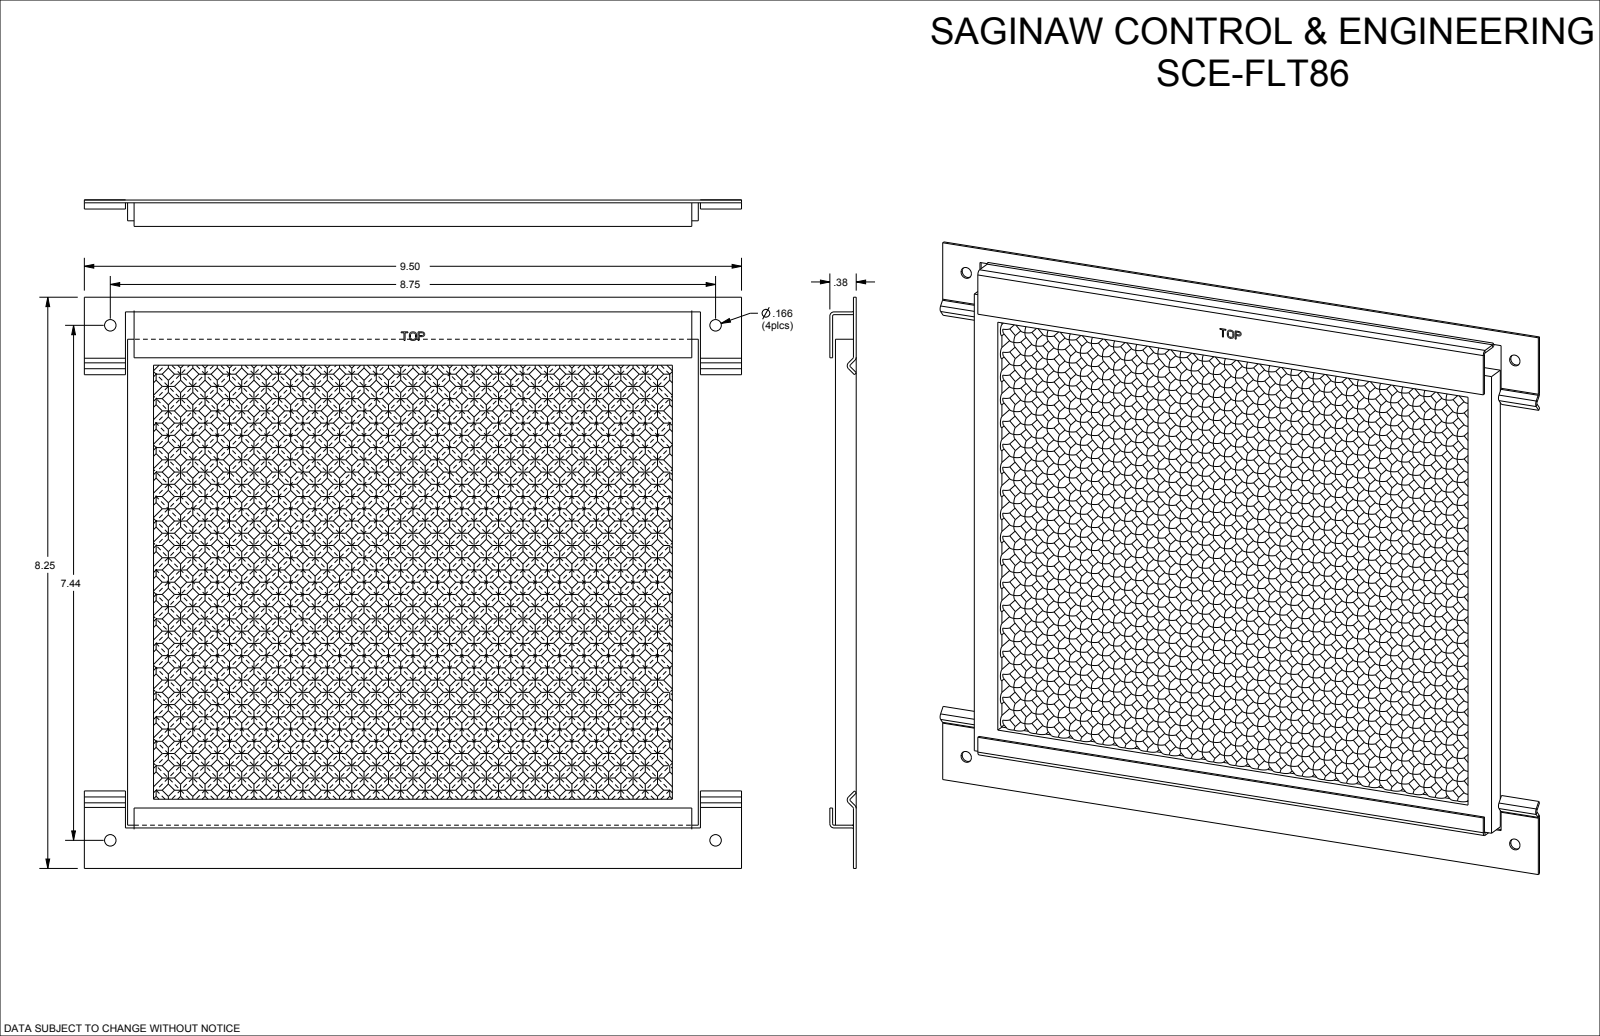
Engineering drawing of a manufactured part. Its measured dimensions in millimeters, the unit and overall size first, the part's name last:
Units: millimetres
Overall size (bounding box): 241.3 × 209.6 × 9.8
Round holes (diameter × count): ⌀4.2 ×4
Round bosses / shafts (diameter × count): ⌀3.2 ×59, ⌀3.2 ×19
Partial cylindrical surfaces — rounded edges, fillets, slot ends (radius × count): R0.5 ×8, R1.5 ×8
Main face-to-face distances: 3.6, 0.5, 4.1, 3.6, 4.1, 7.6, 1, 1, 6.6, 3
Hole centre spacings: 189, 222.3, 291.7
Volume: 131 300 mm³ · Surface area: 129 300 mm²
Bodies: 3 solids, 4714 faces (1662 planar, 3052 cylindrical, 0 other)
Part name (STEP PRODUCT): SCE-FLT86
STEP written by: SolidWorks 2019 (CONFIG_CONTROL_DESIGN)
